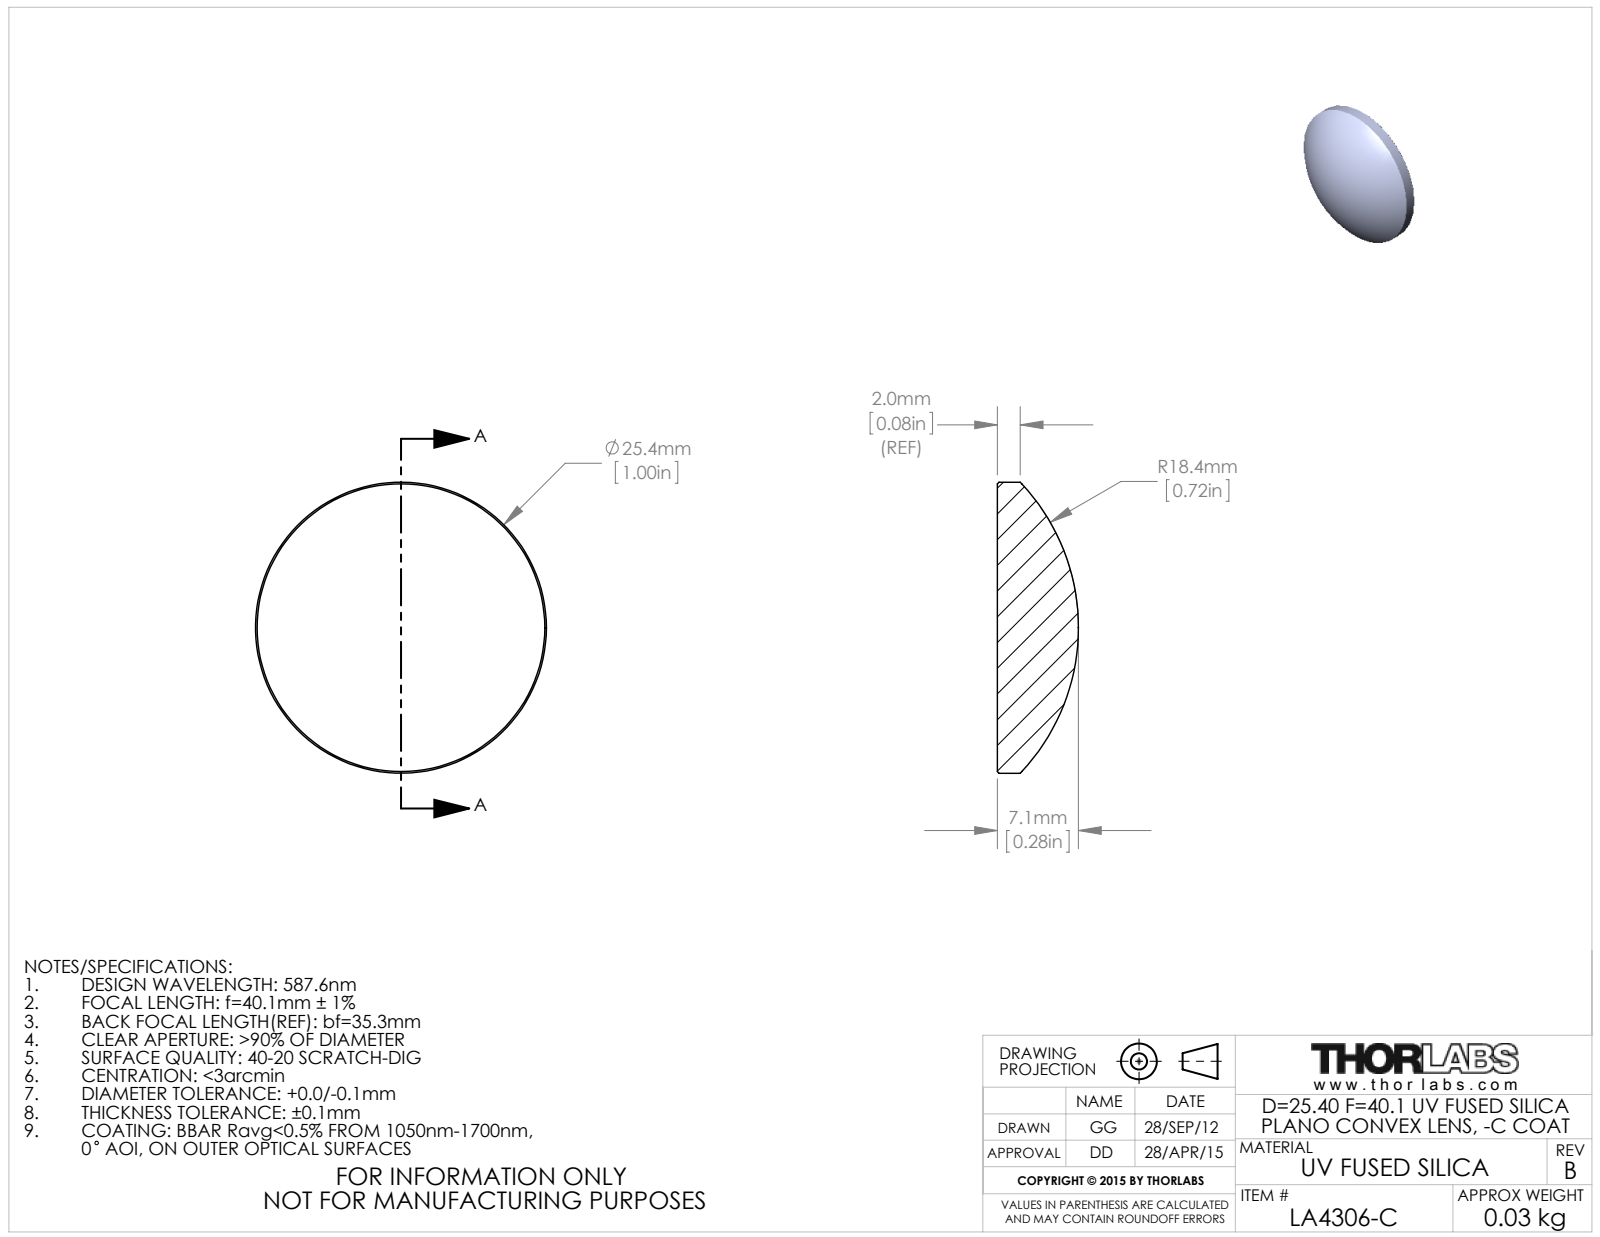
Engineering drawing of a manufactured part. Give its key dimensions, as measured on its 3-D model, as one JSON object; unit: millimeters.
{"part_name": "24998-E0W", "step_written_by": "SolidWorks 2014 (CONFIG_CONTROL_DESIGN)", "units": "millimeters", "bodies": {"solids": 1, "faces": 9, "planar": 1, "cylindrical": 2, "other": 6}, "overall_size": [25.4, 25.4, 7.08], "volume_mm3": 2369, "surface_area_mm2": 1247, "round_bosses_or_shafts": [[25.4, 1]]}
